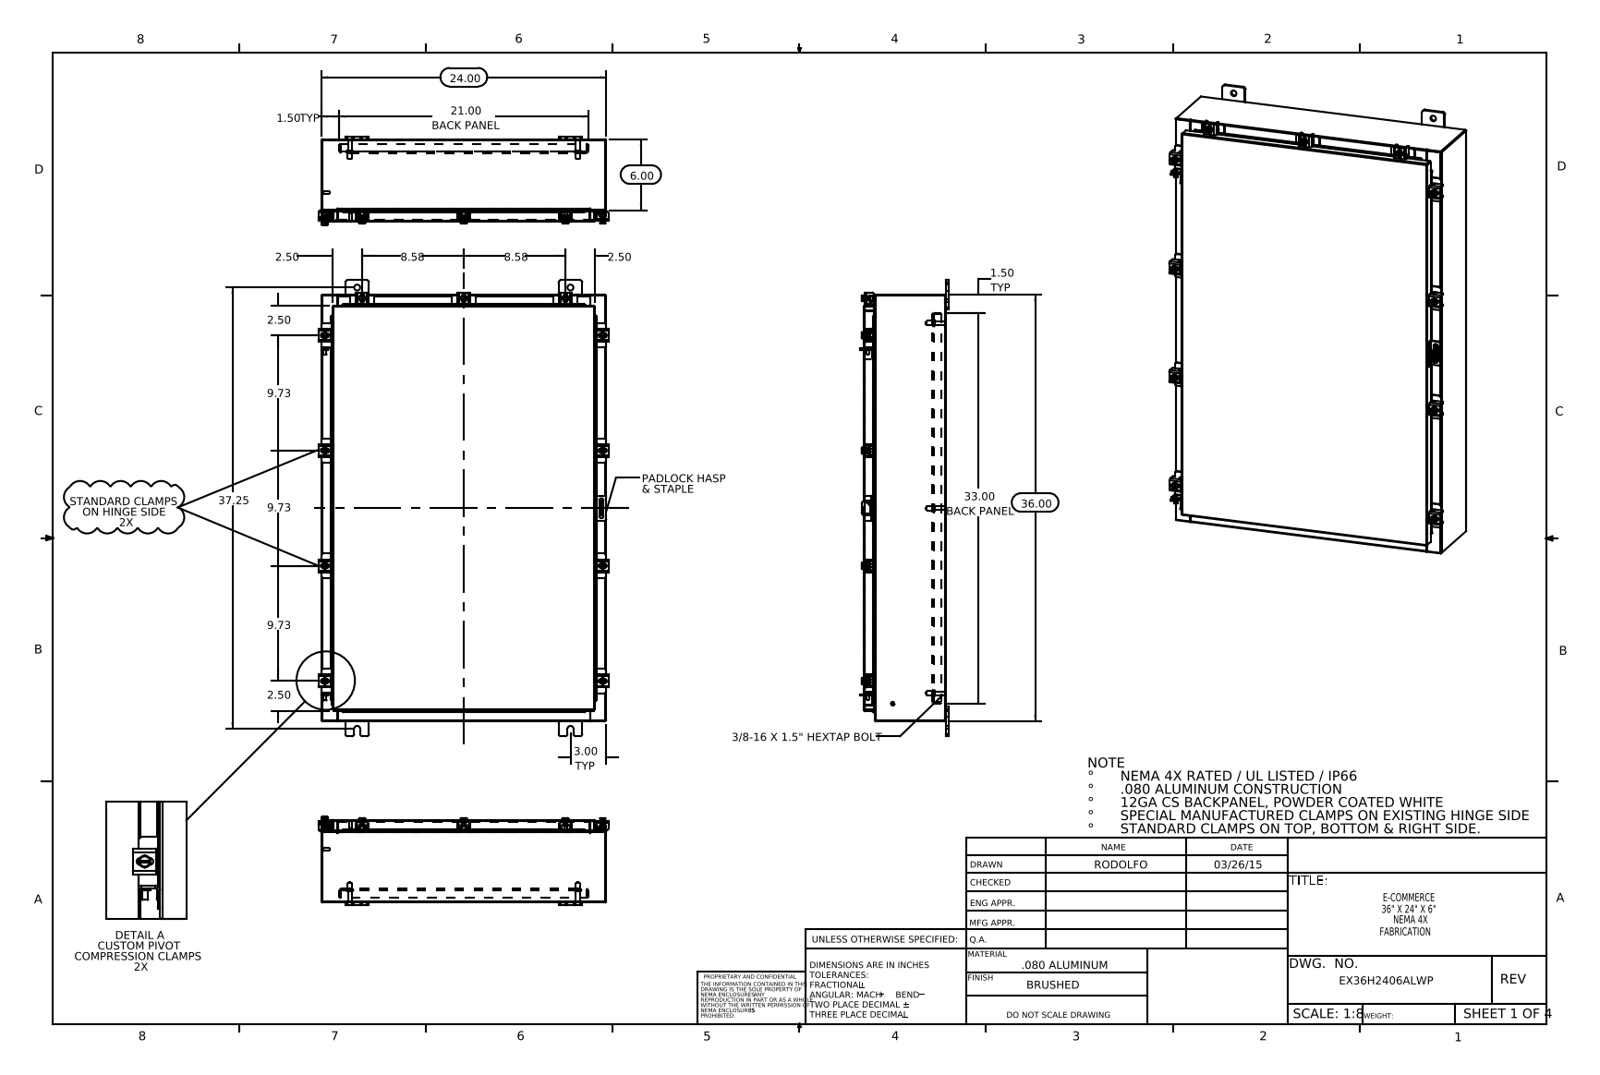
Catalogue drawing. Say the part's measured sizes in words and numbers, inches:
The part is named "EX36H2406ALWP Padlock Staple; EX36H2406ALWP Clamp Bracket; Clamp Top_RTP31; EX36H2406ALWP Top (+8 more)". Its 3-D file was written by "SolidWorks 2014 (CONFIG_CONTROL_DESIGN)". It is 78 solids with 1971 faces: 1041 planar, 758 cylindrical and 172 other. Overall it measures 38.5 by 24.421 by 7.453 inches. Its volume is 290.3 cubic inches and its surface area 7 154 square inches. Round holes: 11 of diameter 0.213, 11 of diameter 0.26, 10 of diameter 0.5, 1 of diameter 0.125, 1 of diameter 0.25. Round bosses or shafts: 11 of diameter 0.5, 11 of diameter 0.25, 9 of diameter 0.399, 6 of diameter 0.625, 6 of diameter 0.375, 6 of diameter 0.33, 2 of diameter 0.315, 2 of diameter 0.236. Partial cylindrical surfaces (rounded edges, fillets, slot ends): 48 of radius 0.06, 26 of radius 0.013, 24 of radius 0.19, 22 of radius 0.088, 22 of radius 0.141, 20 of radius 0.09, 20 of radius 0.12, 19 of radius 0.05. The main face-to-face distances are 0.075, 6.9, 6.975, 6.826, 0.104, 1, 1.075, 5.826, 5.9, 1.179. The hole center spacings are 25.389, 5.299, 9.73, 10.964, 14.744, 15.625, 19.459, 20.597.
